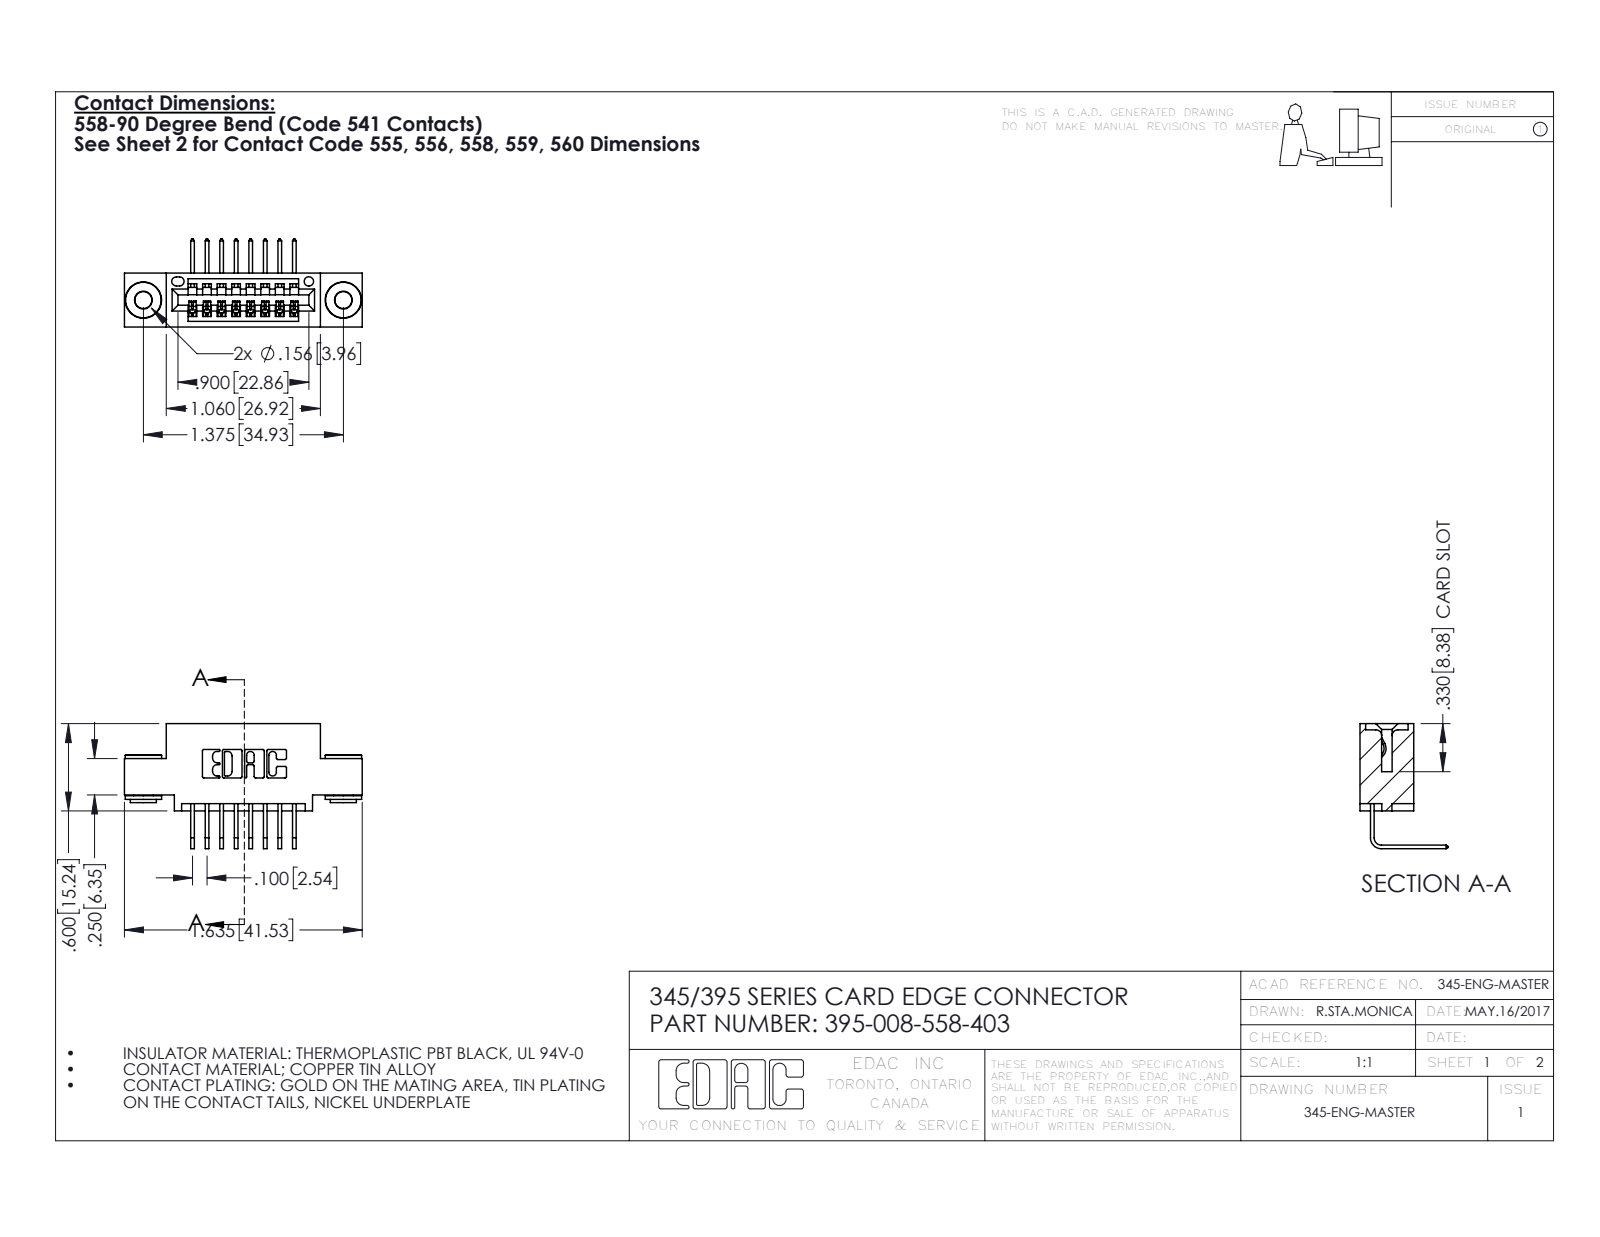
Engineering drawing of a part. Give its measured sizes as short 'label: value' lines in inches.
name: 345-250-002_345-250-002-102; 395-008-558-403; 345 Part_0.110 Offset - 0.156 Dia-TH; 345-292-001_558 Tail - 2
written by: SolidWorks 2016 (CONFIG_CONTROL_DESIGN)
unit: in
bodies: 11 solids, 648 faces (430 planar, 210 cylindrical, 8 other)
size: 1.635 × 0.859 × 0.605
volume: 0.222 in³; area: 7.481 in²
holes: 2× ⌀0.116, 2× ⌀0.156, 1× ⌀0.064
bosses: 2× ⌀0.25, 2× ⌀0.18, 2× ⌀0.136
rounds: 22× R0.01, 16× R0.006, 6× R0.007, 6× R0.031, 3× R0.026, 2× R0.031, 2× R0.04, 1× R0.014
face distances: 0.2, 0.37, 0.1, 0.072, 0.298, 0.025, 0.3, 0.16, 0.098, 0.272
hole spacings: 0.27, 1.144, 1.375
